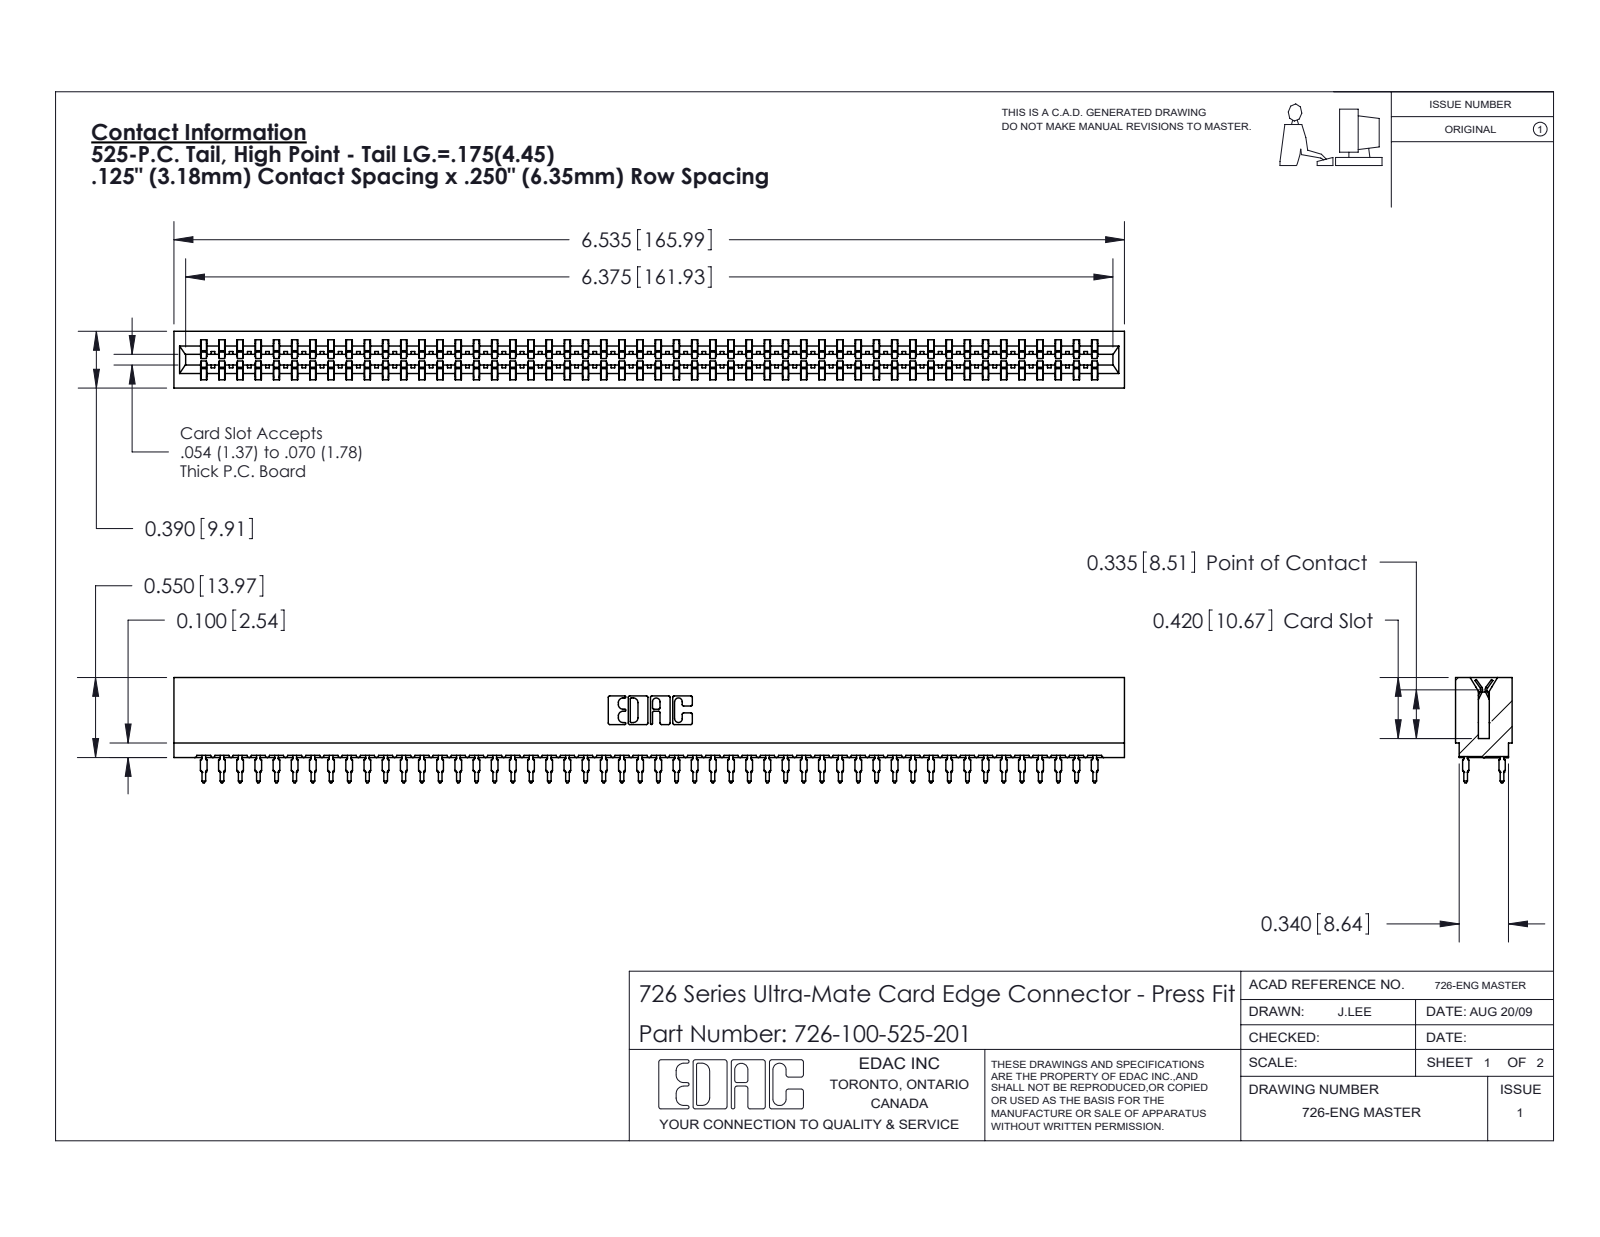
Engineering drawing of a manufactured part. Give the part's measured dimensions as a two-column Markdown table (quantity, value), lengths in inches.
| quantity | value |
| --- | --- |
| part name | 746-292-001_525; 726 Part_.515 Slot Depth - 01; 726-100-525-201 |
| STEP written by | SolidWorks 2020 (CONFIG_CONTROL_DESIGN) |
| units | inches |
| bodies | 101 solids, 9047 faces (4655 planar, 1792 cylindrical, 2600 other) |
| overall size | 6.535 × 0.724 × 0.39 |
| volume | 0.926 in³ |
| surface area | 39.08 in² |
| partial cylindrical surfaces (radius × count) | 0.021 × 200, 0.015 × 51, 0.01 × 22, 0.005 × 8, 0.011 × 8, 0.007 × 6, 0.031 × 6, 0.026 × 3 |
| main face-to-face distances | 0.057, 0.333, 0.39, 0.025, 0.307, 0.25, 0.275, 0.083, 0.365, 0.032 |
